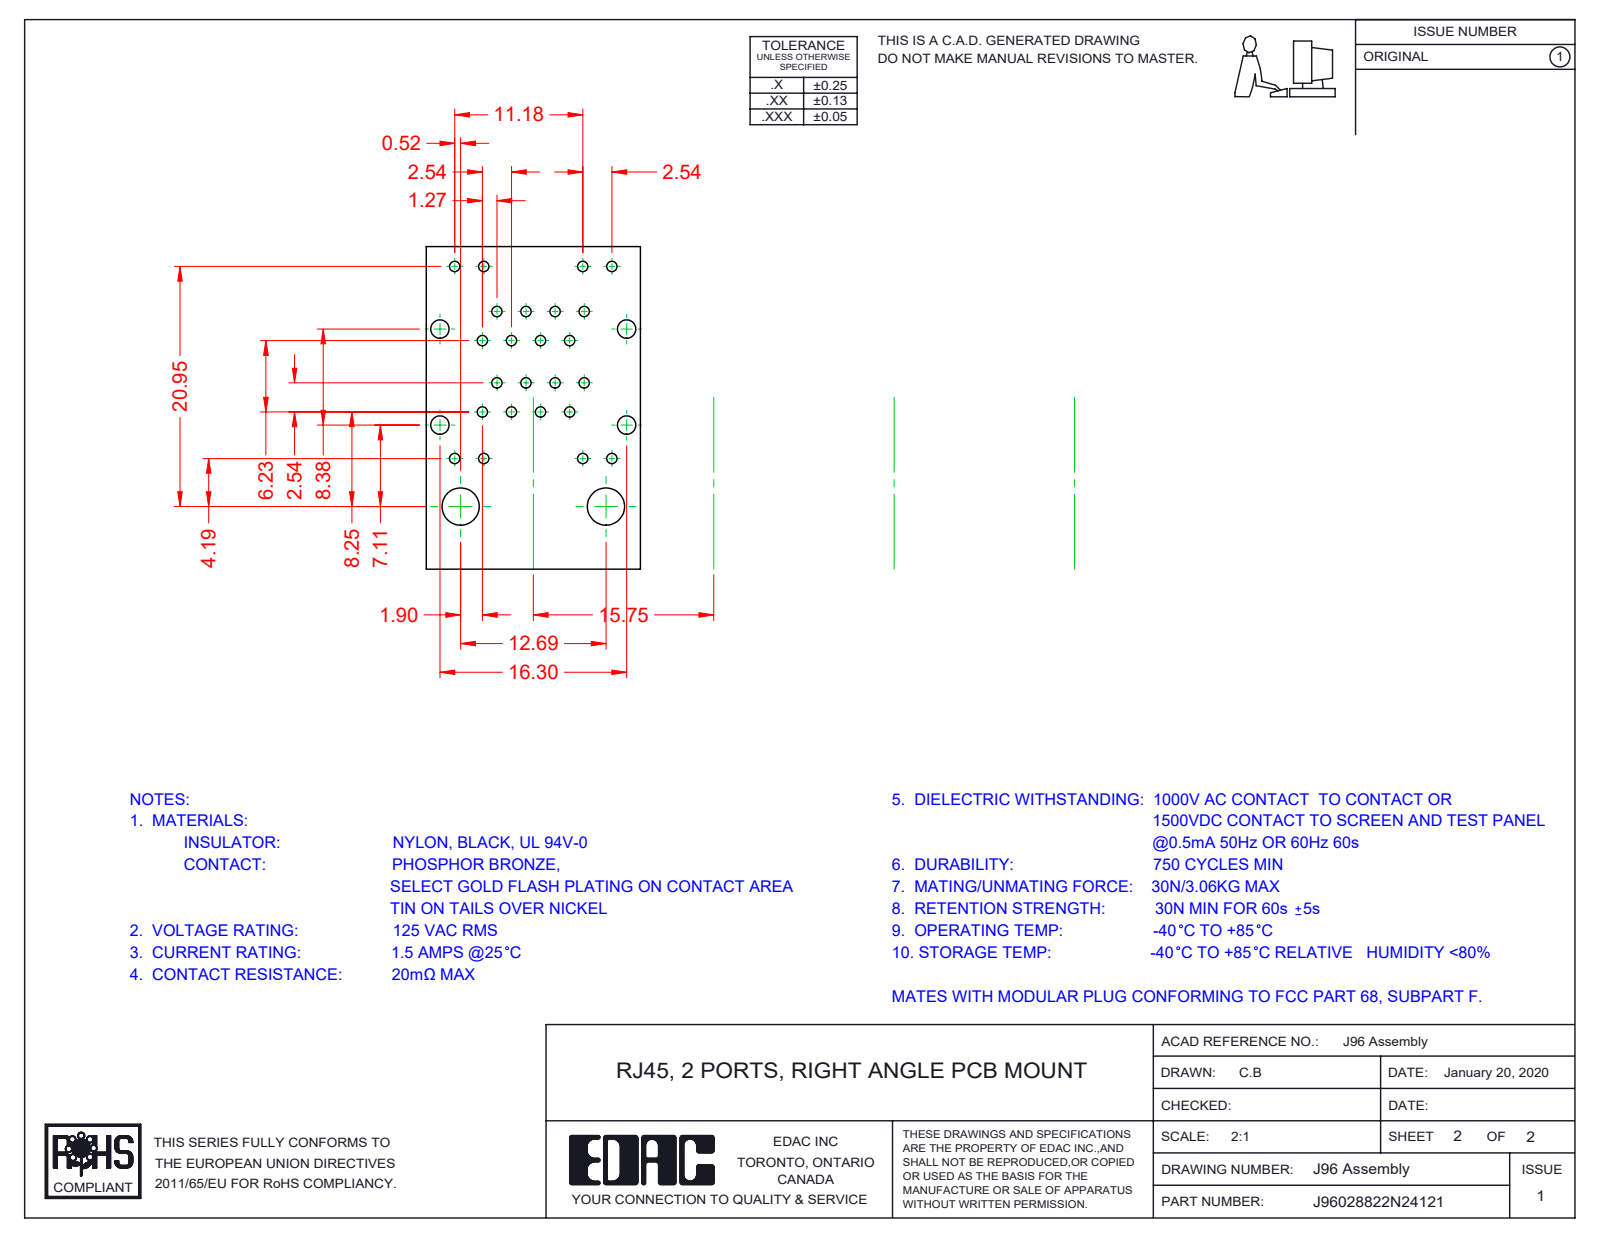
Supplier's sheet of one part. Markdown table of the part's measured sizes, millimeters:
| quantity | value |
| --- | --- |
| part name | 96 Back Plate_2 Ports; 96 LED LH Upper_2-Red; 96 Insulator_2 Ports; 96 Contacts Upper (+8 more) |
| STEP written by | SolidWorks 2016 (CONFIG_CONTROL_DESIGN) |
| units | millimeters |
| bodies | 27 solids, 2382 faces (1849 planar, 427 cylindrical, 106 other) |
| overall size | 29.58 × 28.68 × 16.8 |
| volume | 6 852 mm³ |
| surface area | 19 109 mm² |
| partial cylindrical surfaces (radius × count) | 0.25 × 48, 0.15 × 32, 0.35 × 24, 0.5 × 16, 1 × 16, 0.2 × 13, 0.7 × 9, 2 × 5 |
| main face-to-face distances | 16.3, 16.1, 1.75, 16.5, 14.75, 1.55, 14.55, 0.53, 1.48, 11.2 |
